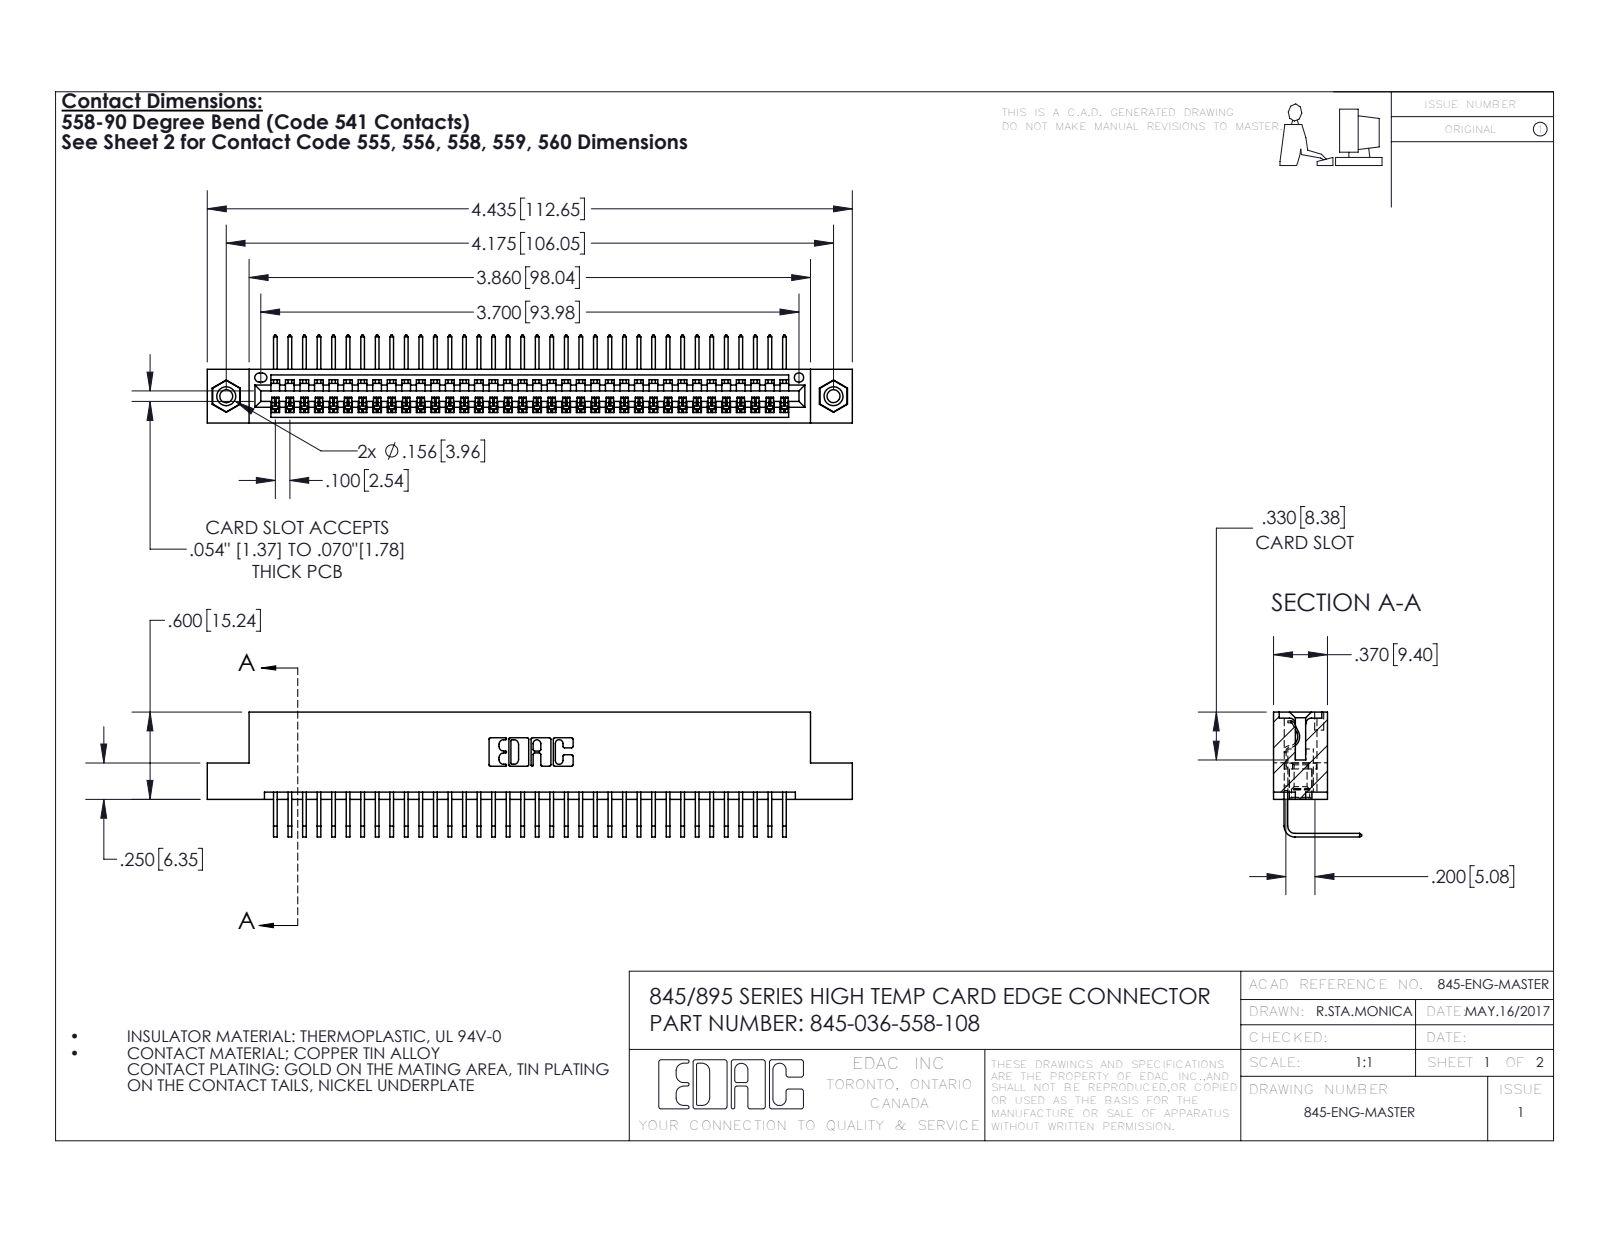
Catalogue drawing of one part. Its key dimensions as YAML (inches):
part_name: "345-292-001_558 Tail - 2; 345-036-558-108; 345-250-001_345-250-003-102; 345 Part_Flush Mounting Lugs - 0.156 Dia-TI"
step_written_by: "SolidWorks 2016 (CONFIG_CONTROL_DESIGN)"
units: inches
bodies: {solids: 39, faces: 2346, planar: 1624, cylindrical: 706, other: 16}
overall_size: [4.435, 0.859, 0.605]
volume: 0.657
surface_area: 23.17
round_holes:
  - {diameter: 0.089, count: 2}
  - {diameter: 0.125, count: 2}
  - {diameter: 0.156, count: 2}
  - {diameter: 0.064, count: 1}
round_bosses_or_shafts:
  - {diameter: 0.155, count: 2}
partial_cylinders:
  - {radius: 0.006, count: 72}
  - {radius: 0.01, count: 22}
  - {radius: 0.007, count: 6}
  - {radius: 0.031, count: 6}
  - {radius: 0.026, count: 3}
  - {radius: 0.031, count: 2}
  - {radius: 0.04, count: 2}
  - {radius: 0.014, count: 1}
face_to_face_distances: [0.072, 0.298, 0.37, 0.2, 0.098, 0.272, 0.025, 0.225, 0.149, 0.072]
hole_center_spacings: [0.27, 3.939, 4.175]
